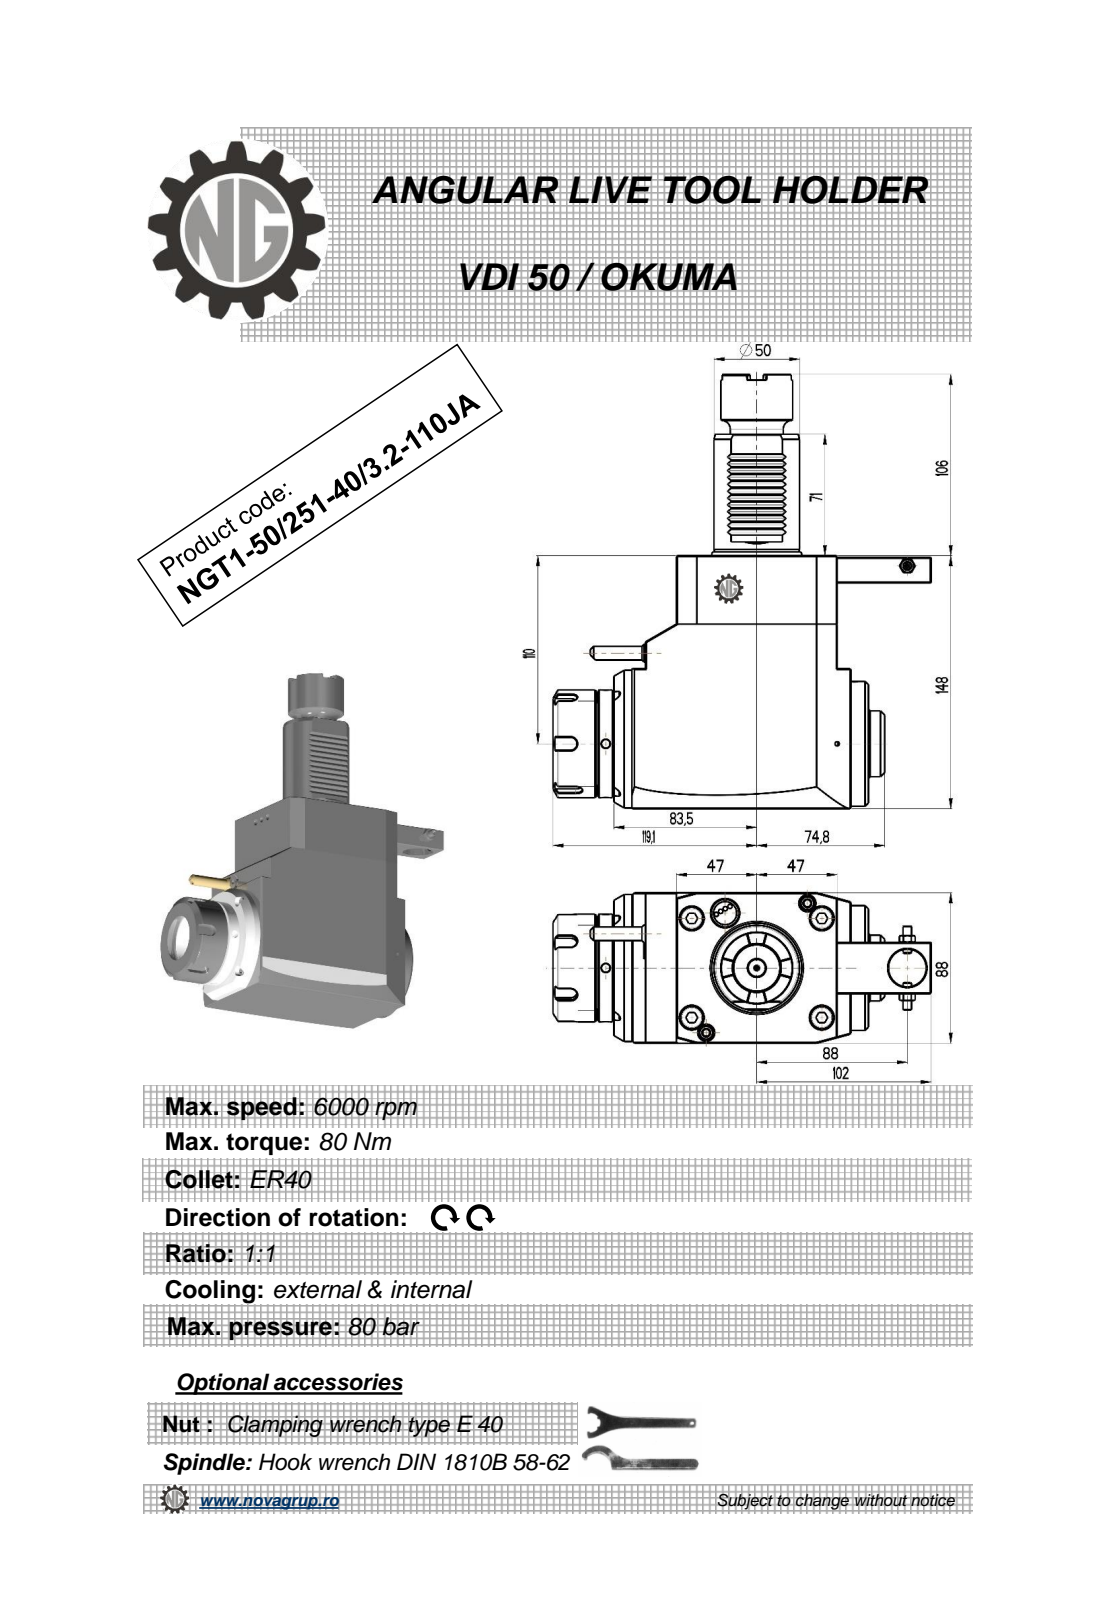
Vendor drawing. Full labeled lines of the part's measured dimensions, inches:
Part name (STEP PRODUCT): NGT1_50_251_40_3_2_110JA
STEP written by: PRO/ENGINEER BY PARAMETRIC TECHNOLOGY CORPORATION, 2010280 (CONFIG_CONTROL_DESIGN)
Units: inches
Bodies: 1 solid, 480 faces (221 planar, 100 cylindrical, 159 other)
Overall size (bounding box): 10 × 8.705 × 3.465
Volume: 115.1 in³ · Surface area: 189.6 in²
Round holes (diameter × count): ⌀0.197 ×3, ⌀0.118 ×1, ⌀0.177 ×1, ⌀0.374 ×1, ⌀0.866 ×1, ⌀1.102 ×1, ⌀1.319 ×1
Round bosses / shafts (diameter × count): ⌀3.386 ×1, ⌀2.874 ×1, ⌀2.48 ×1, ⌀2.008 ×1, ⌀1.969 ×1, ⌀1.654 ×1, ⌀1.575 ×1, ⌀1.516 ×1
Partial cylindrical surfaces — rounded edges, fillets, slot ends (radius × count): R0.01 ×12, R0.012 ×12, R0.008 ×6, R0.148 ×5
Main face-to-face distances: 3.465, 5.827, 0.315, 3.701, 4.016, 1.437, 5.138, 4.724, 5.858, 4.421
Hole centre spacings: 2.065, 2.23, 3.465, 3.474, 3.996, 6.939
